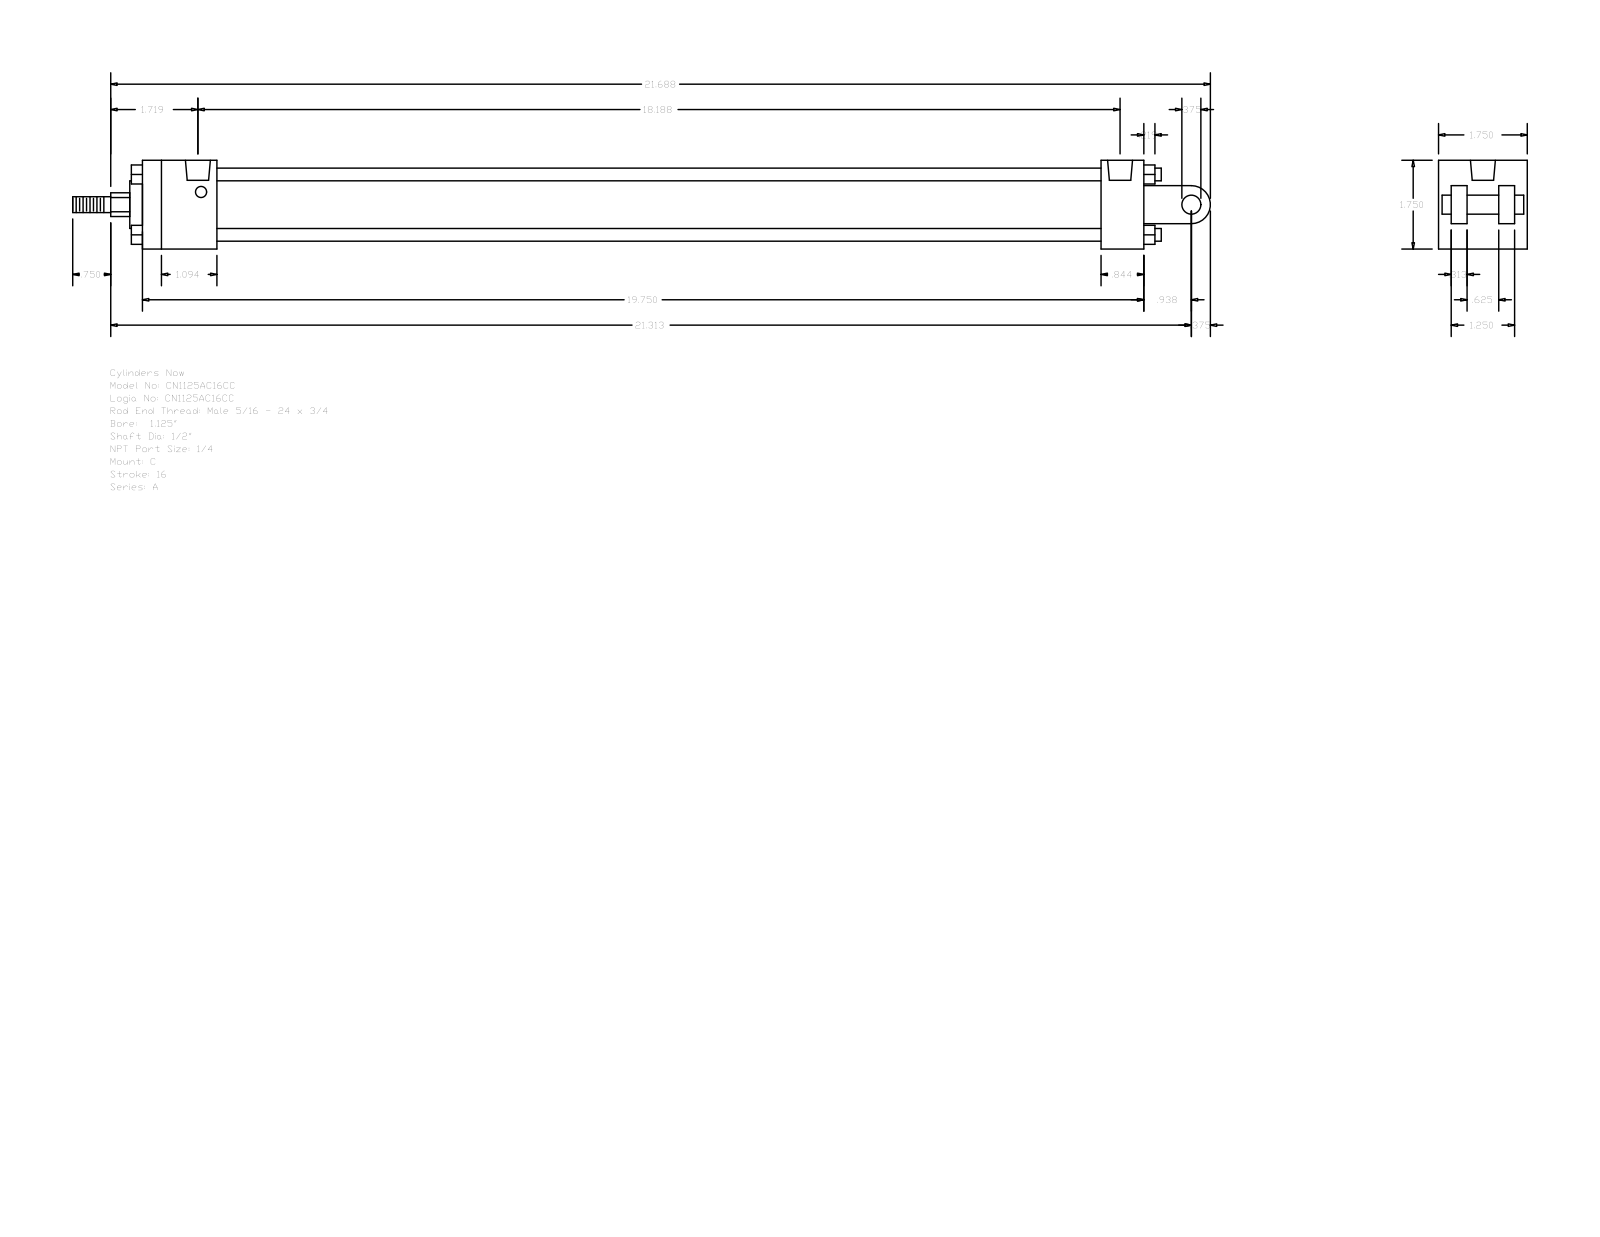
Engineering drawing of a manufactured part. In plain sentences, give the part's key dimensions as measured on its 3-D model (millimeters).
The part is named "A_C__0112_0.5". Its 3-D file was written by "GSSL Pune (CONFIG_CONTROL_DESIGN)". It is 0 solids with 135 faces: 102 planar, 33 cylindrical and 0 other. Overall it measures 569.91 by 44.45 by 44.45 millimeters. Round holes: 4 of diameter 5.56, 2 of diameter 12.49. Round bosses or shafts: 4 of diameter 6.35, 1 of diameter 31.88, 1 of diameter 23.81, 1 of diameter 12.7, 1 of diameter 9.53, 1 of diameter 7.94. Partial cylindrical surfaces (rounded edges, fillets, slot ends): 1 of radius 5.94, 1 of radius 9.53. The main face-to-face distances are 44.46, 6.35, 31.76, 14.29, 501.64, 30.17, 480.21, 21.43, 37.3, 442.91. The hole center spacings are 458.79, 1.58, 1.59, 460.37, 460.38, 461.96.
